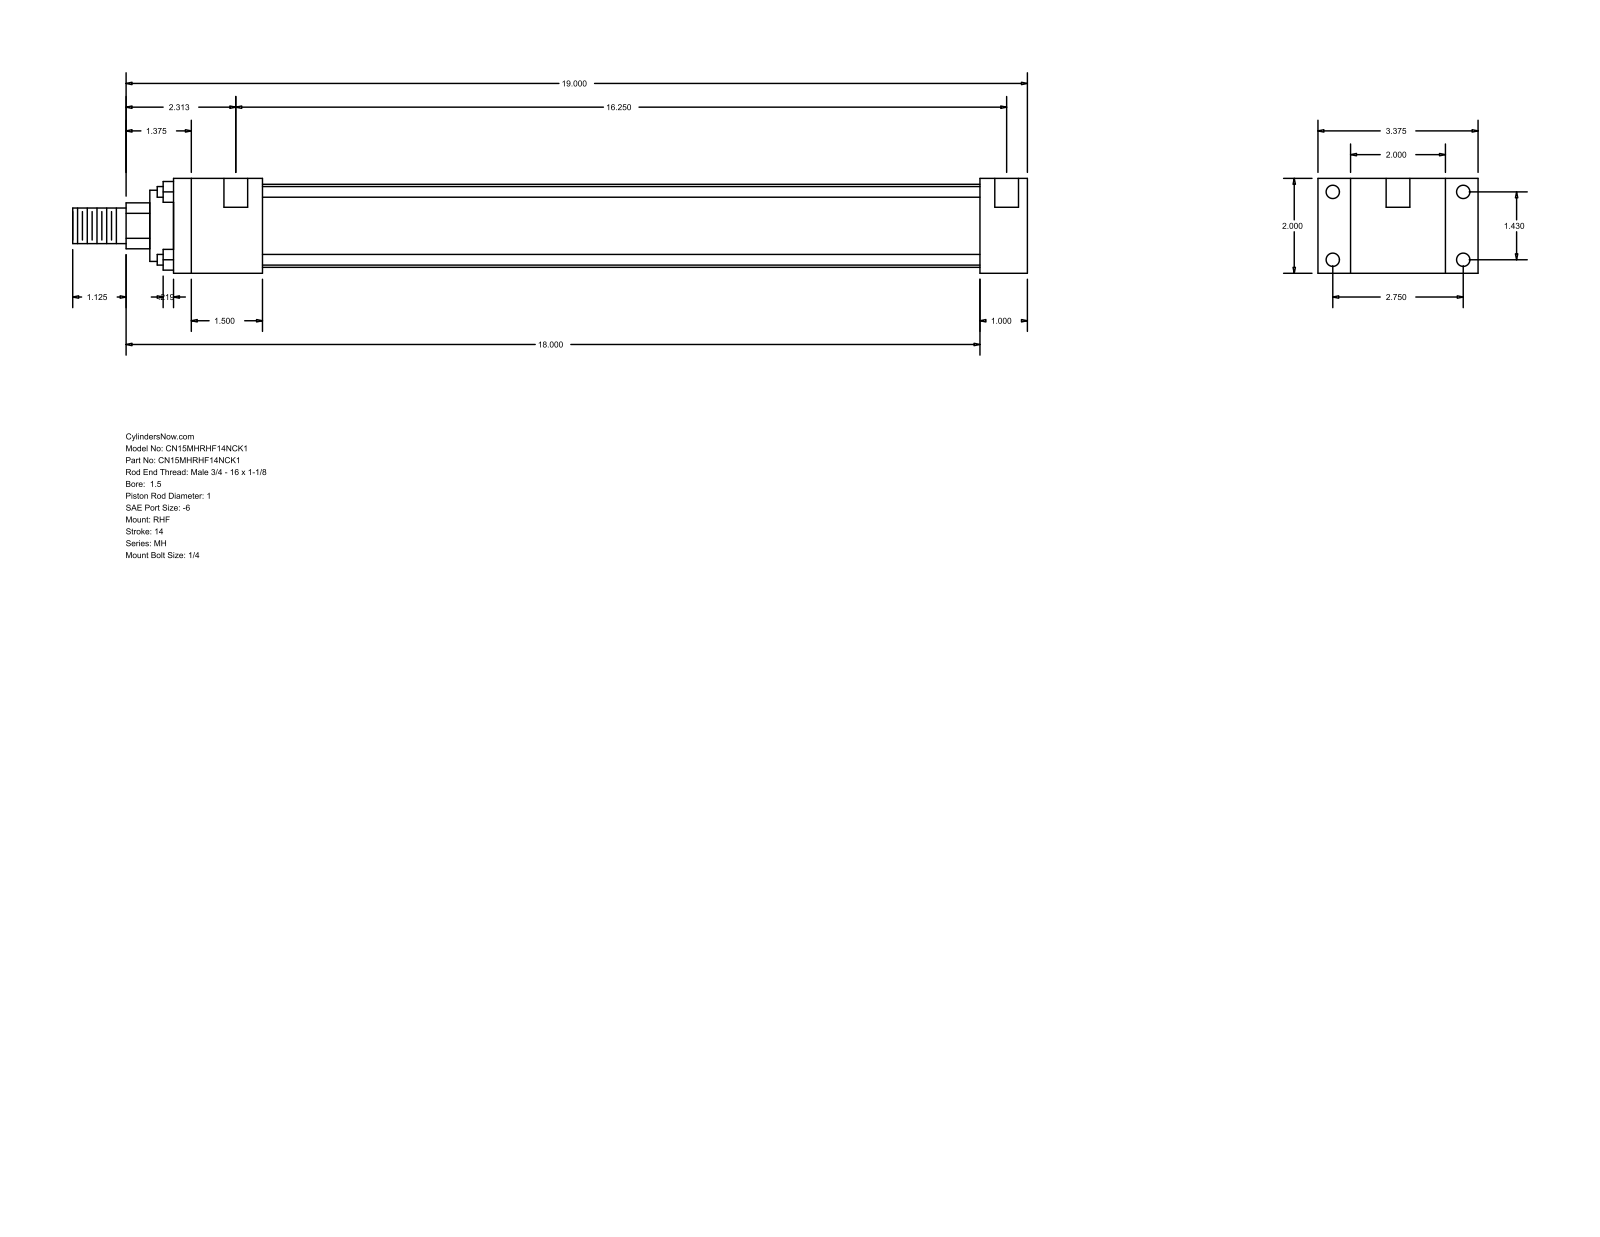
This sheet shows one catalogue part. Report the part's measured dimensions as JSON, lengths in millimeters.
{"part_name": "MH_RHF__0150_1", "step_written_by": "GSSL Pune (CONFIG_CONTROL_DESIGN)", "units": "millimeters", "bodies": {"solids": 0, "faces": 88, "planar": 60, "cylindrical": 28, "other": 0}, "overall_size": [511.18, 85.72, 50.8], "round_holes": [[5.56, 4], [7.14, 4], [12.7, 2]], "round_bosses_or_shafts": [[5.71, 4], [44.45, 1], [38.1, 1], [25.4, 1], [19.05, 1]], "partial_cylinders_radius": [[12.29, 1]], "face_to_face_distances": [50.8, 25.4, 17.46, 68.26, 85.72, 457.2, 431.8, 47.63, 384.17, 409.57], "hole_center_spacings": [36.32, 69.84, 78.72, 415.93, 3.18, 412.75]}
